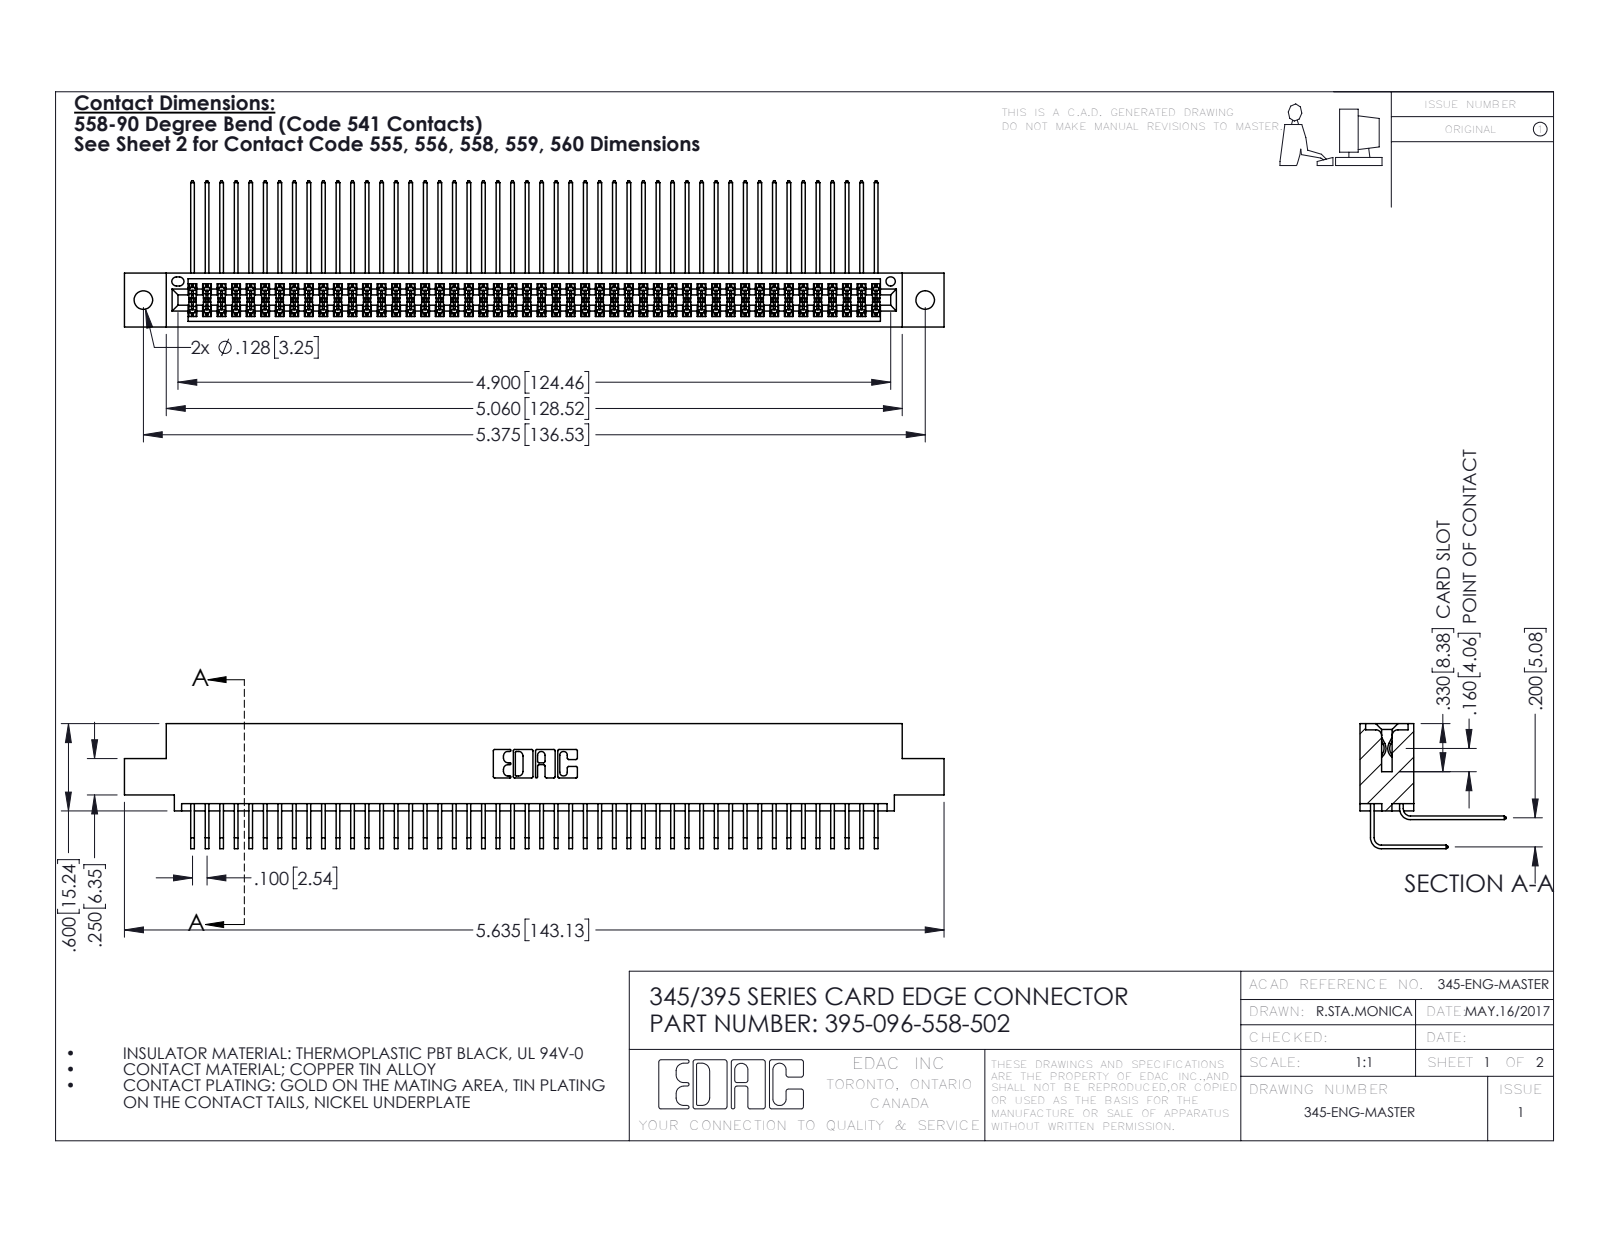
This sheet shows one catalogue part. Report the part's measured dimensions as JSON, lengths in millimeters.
{"part_name": "345-292-001_558 Tail - 2; 345 Part_0.110 Offset - 0.128 Dia; 345-292-001_558 559 Tail - 1; 395-096-558-502", "step_written_by": "SolidWorks 2016 (CONFIG_CONTROL_DESIGN)", "units": "millimeters", "bodies": {"solids": 97, "faces": 5122, "planar": 3444, "cylindrical": 1678, "other": 0}, "overall_size": [143.1, 25.5, 21.8], "volume_mm3": 14400, "surface_area_mm2": 23830, "round_holes": [[3.3, 2], [1.6, 1]], "partial_cylinders_radius": [[0.2, 145], [0.3, 22], [0.2, 6], [0.8, 6], [0.7, 3], [0.4, 2], [0.5, 2], [0.6, 2]], "face_to_face_distances": [1.8, 7.6, 5.1, 9.4, 2.5, 6.9, 0.6, 5.7, 0.6, 4.4], "hole_center_spacings": [6.9, 130.5, 136.5]}
